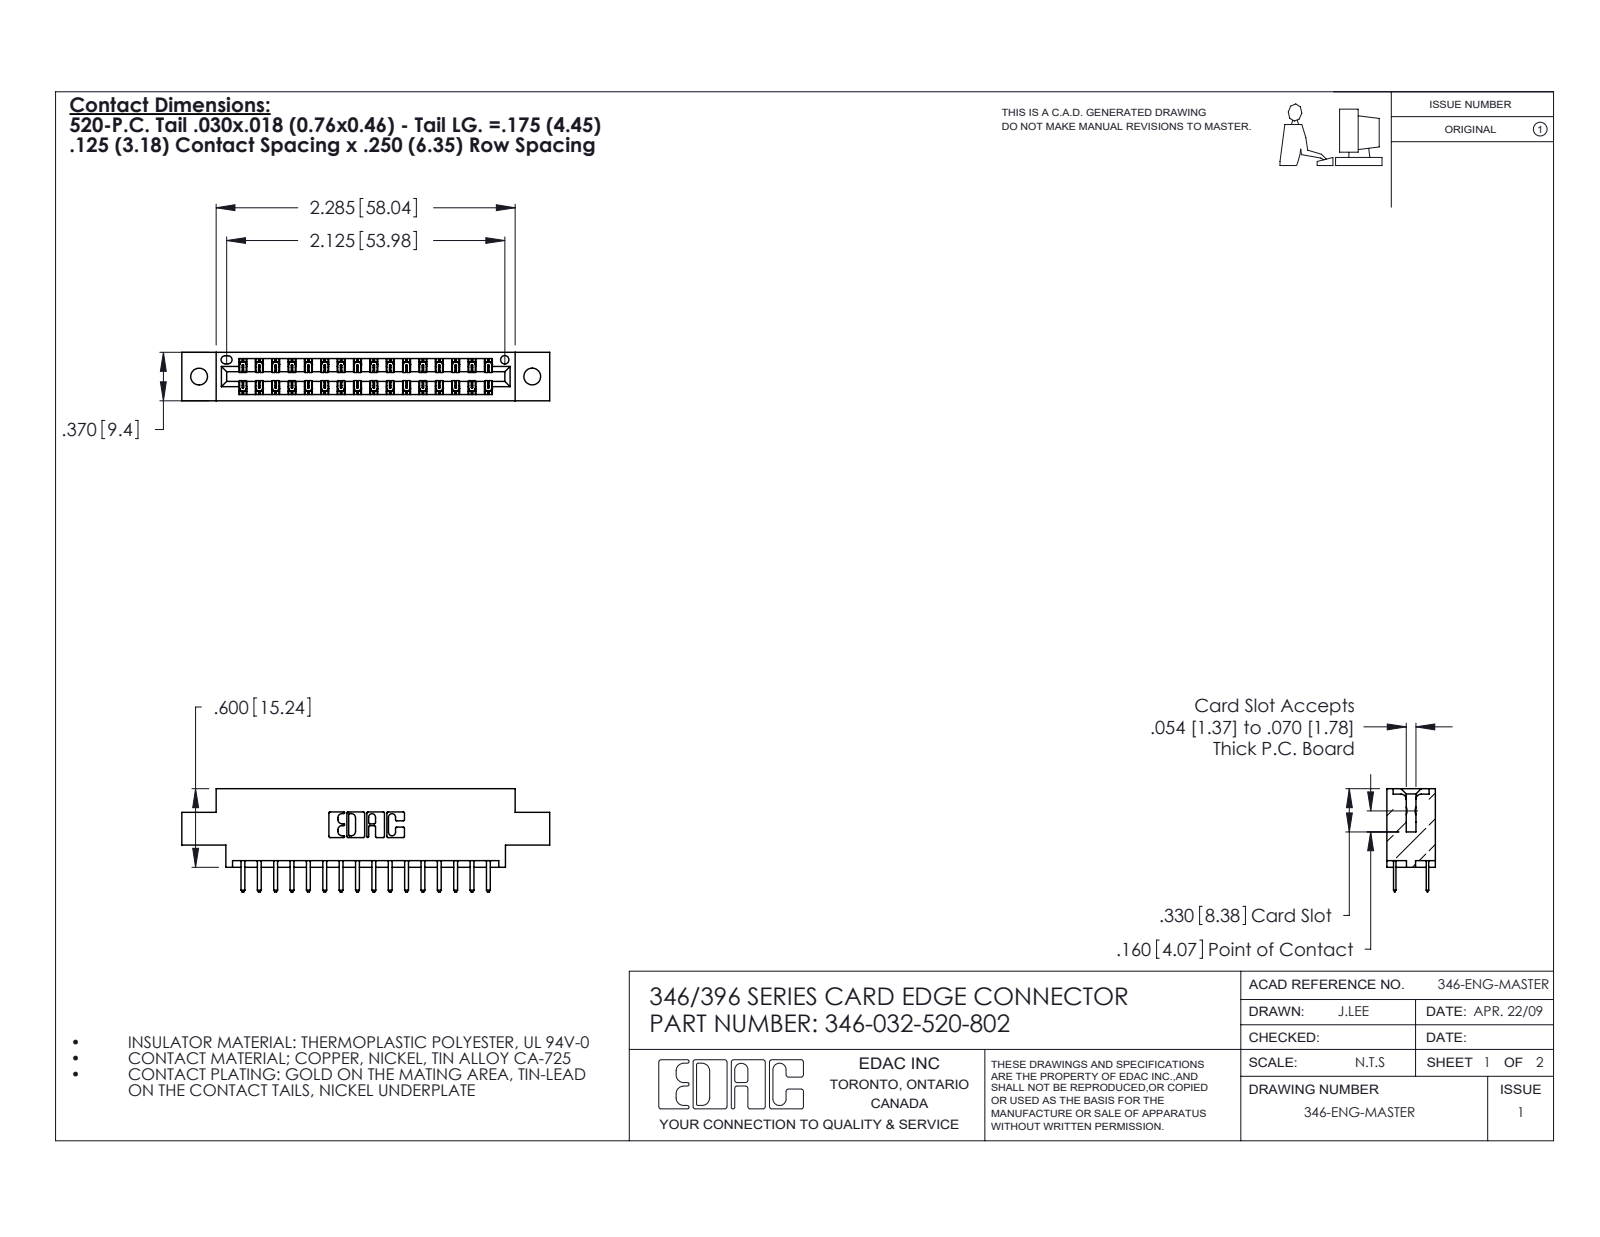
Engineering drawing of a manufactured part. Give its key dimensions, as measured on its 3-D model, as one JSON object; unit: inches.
{"part_name": "346-032-520-802; 346 Part_0.170 Offset - 0.128 Dia; 345-292-001_345-293-120", "step_written_by": "SolidWorks 2020 (CONFIG_CONTROL_DESIGN)", "units": "inches", "bodies": {"solids": 33, "faces": 1918, "planar": 1264, "cylindrical": 654, "other": 0}, "overall_size": [2.81, 0.788, 0.37], "volume_in3": 0.4, "surface_area_in2": 13.14, "round_holes": [[0.128, 2], [0.064, 1]], "partial_cylinders_radius": [[0.006, 48], [0.01, 36], [0.01, 22], [0.007, 6], [0.031, 6], [0.026, 3], [0.014, 2], [0.022, 2]], "face_to_face_distances": [0.25, 0.048, 0.322, 0.37, 0.275, 0.072, 0.298, 0.025, 0.148, 0.222], "hole_center_spacings": [0.246, 2.338, 2.545]}
